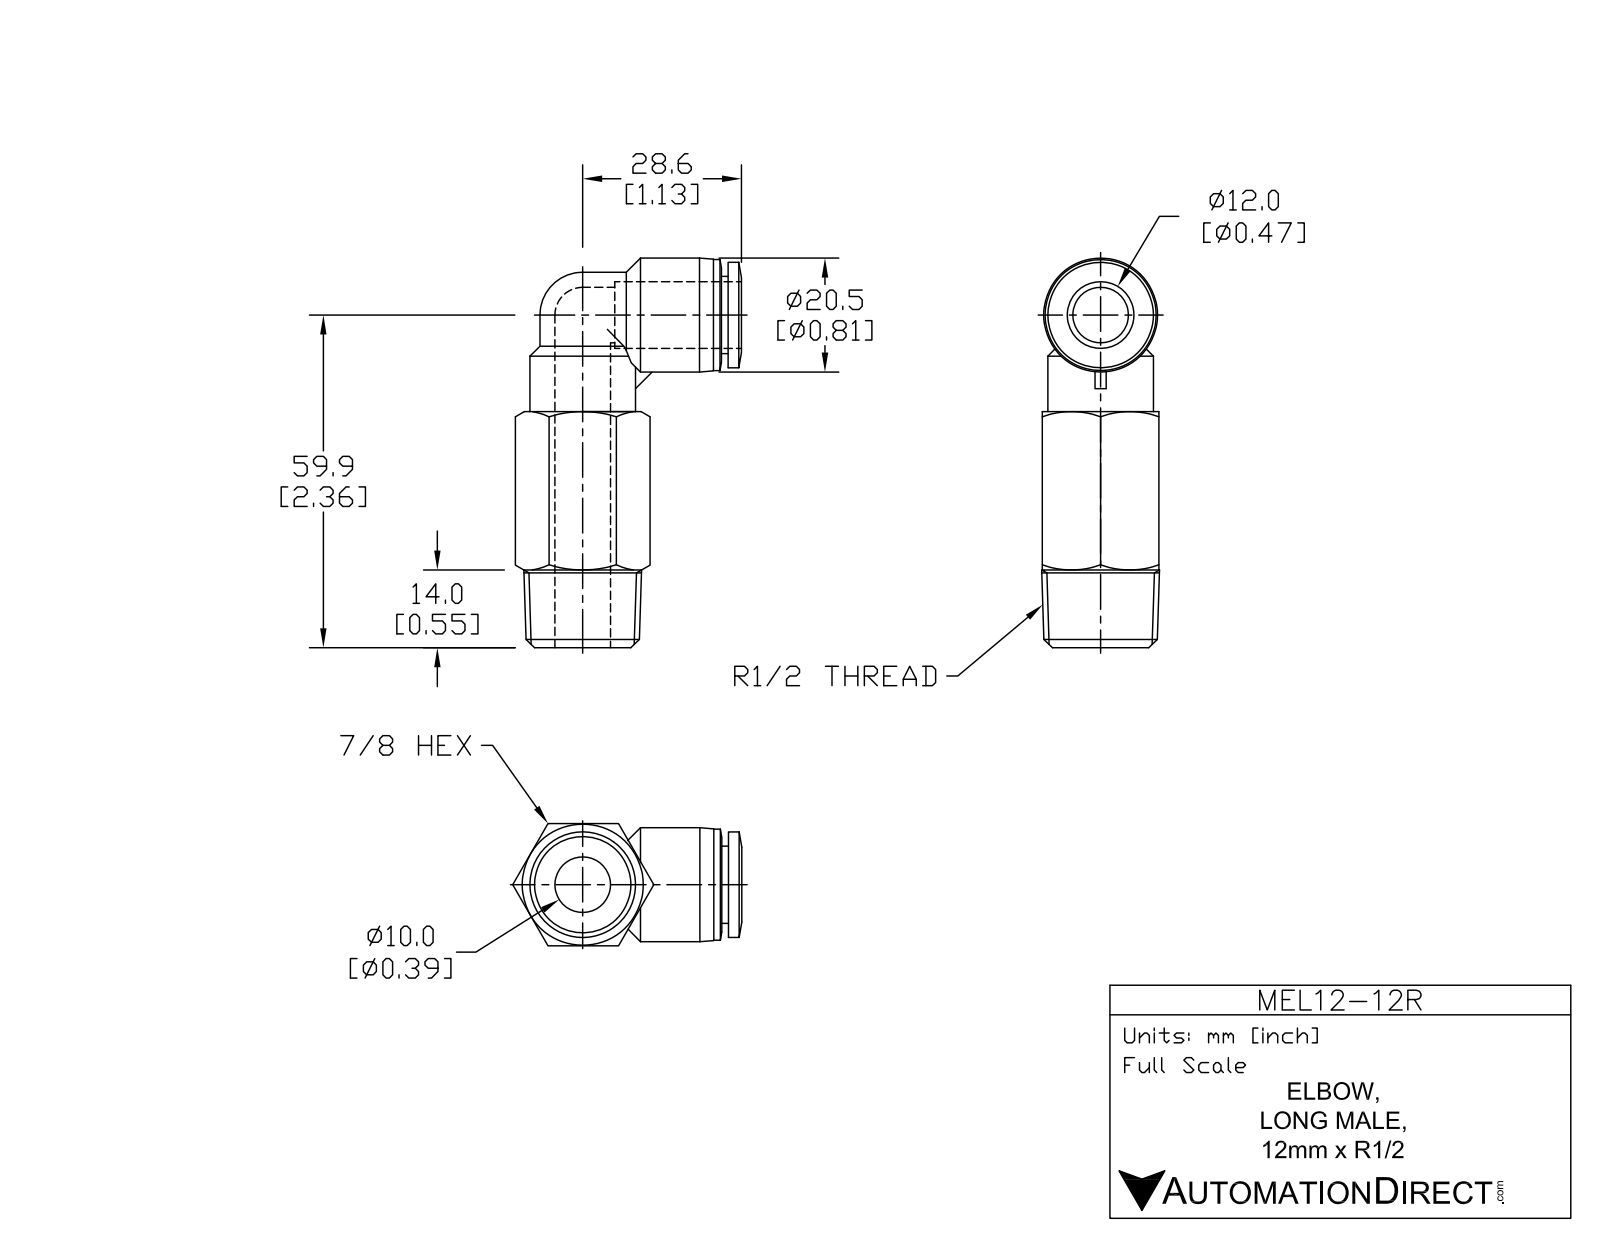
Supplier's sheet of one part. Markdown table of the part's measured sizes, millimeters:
| quantity | value |
| --- | --- |
| part name | MEL12M-12R |
| STEP written by | SolidWorks 2015 (AUTOMOTIVE_DESIGN) |
| units | millimeters |
| bodies | 1 solid, 69 faces (17 planar, 19 cylindrical, 33 other) |
| overall size | 70.2 × 41.4 × 22 |
| volume | 20 500 mm³ |
| surface area | 9 439 mm² |
| round holes (diameter × count) | 10 × 2, 12.3 × 1 |
| round bosses / shafts (diameter × count) | 19 × 2, 20.5 × 1, 20 × 1, 15.4 × 1, 13.9 × 1 |
| partial cylindrical surfaces (radius × count) | 7.7 × 1 |
| main face-to-face distances | 22, 41.5, 1.2, 19.3, 20.5, 14, 27.5, 22.9, 3.6, 2.4 |
